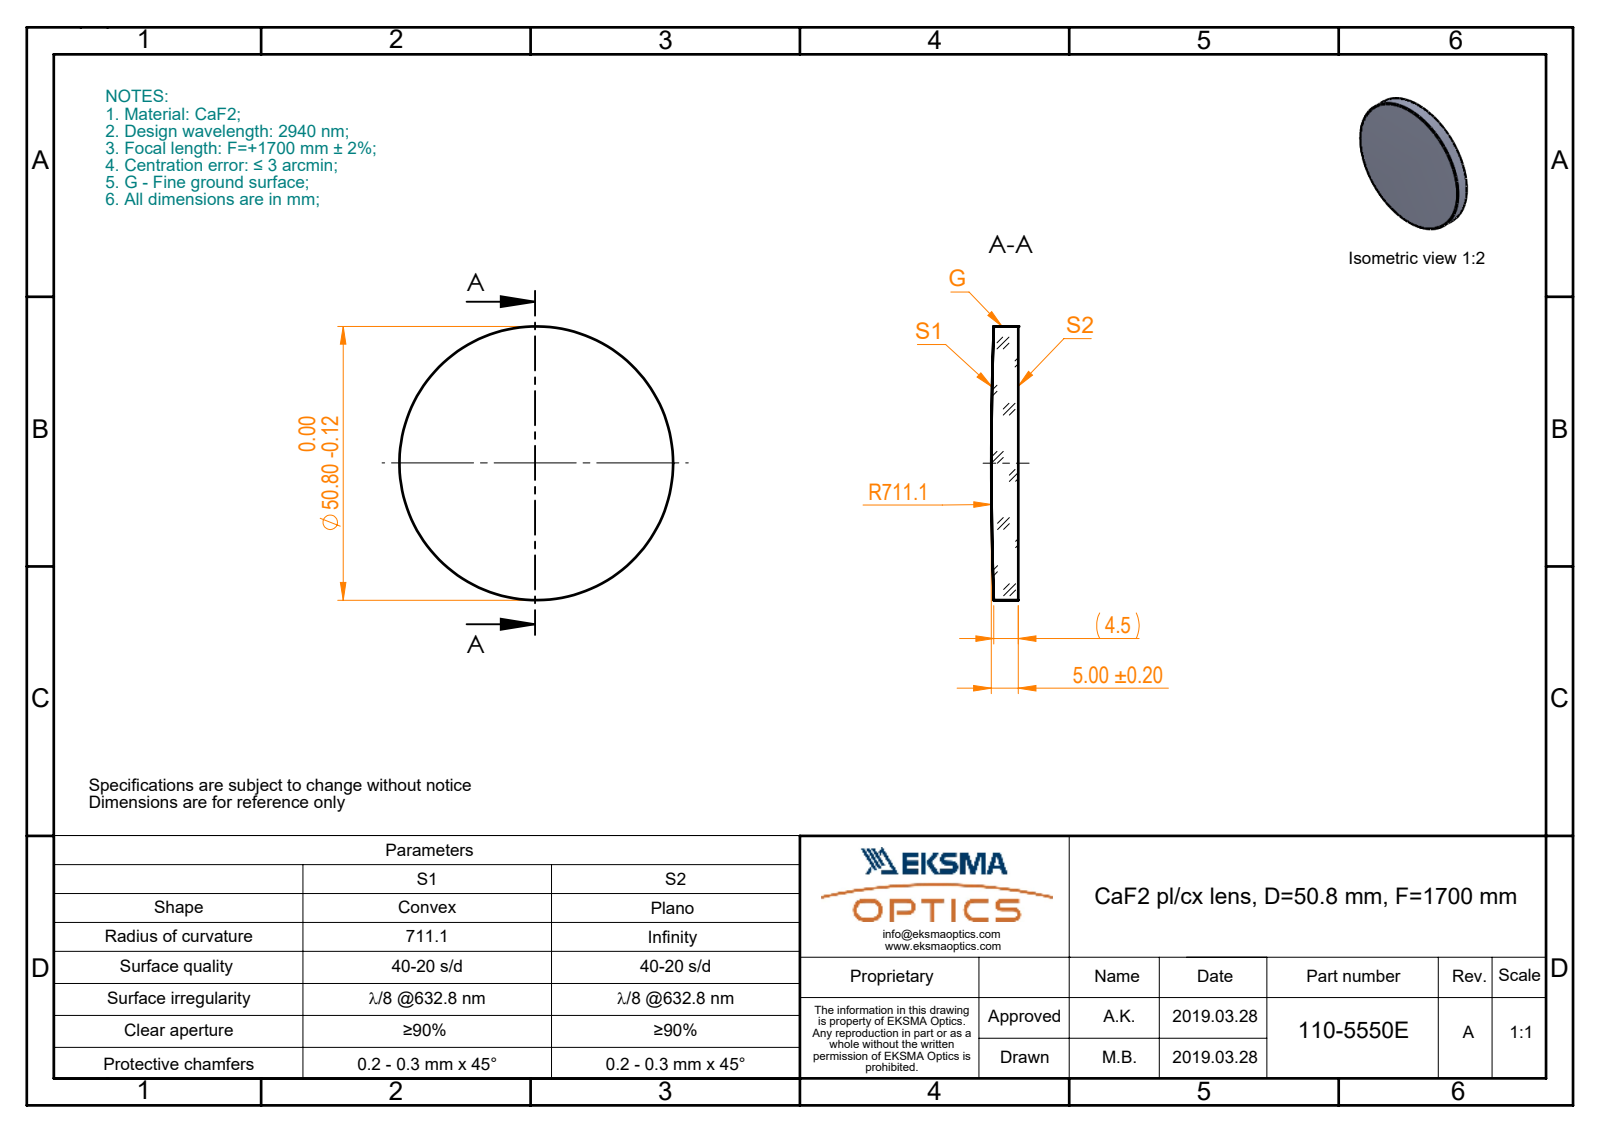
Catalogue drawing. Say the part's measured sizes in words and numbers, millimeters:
The part is named "110-5550E CaF2 pl-cx 50.8 F1700". Its 3-D file was written by "SolidWorks 2017 (CONFIG_CONTROL_DESIGN)". It is 1 solid with 5 faces: 1 planar, 2 cylindrical and 2 other. Overall it measures 50.8 by 50.8 by 5 millimeters. Its volume is 9 674 cubic millimeters and its surface area 4 780 square millimeters. Round bosses or shafts: 1 of diameter 50.8.
